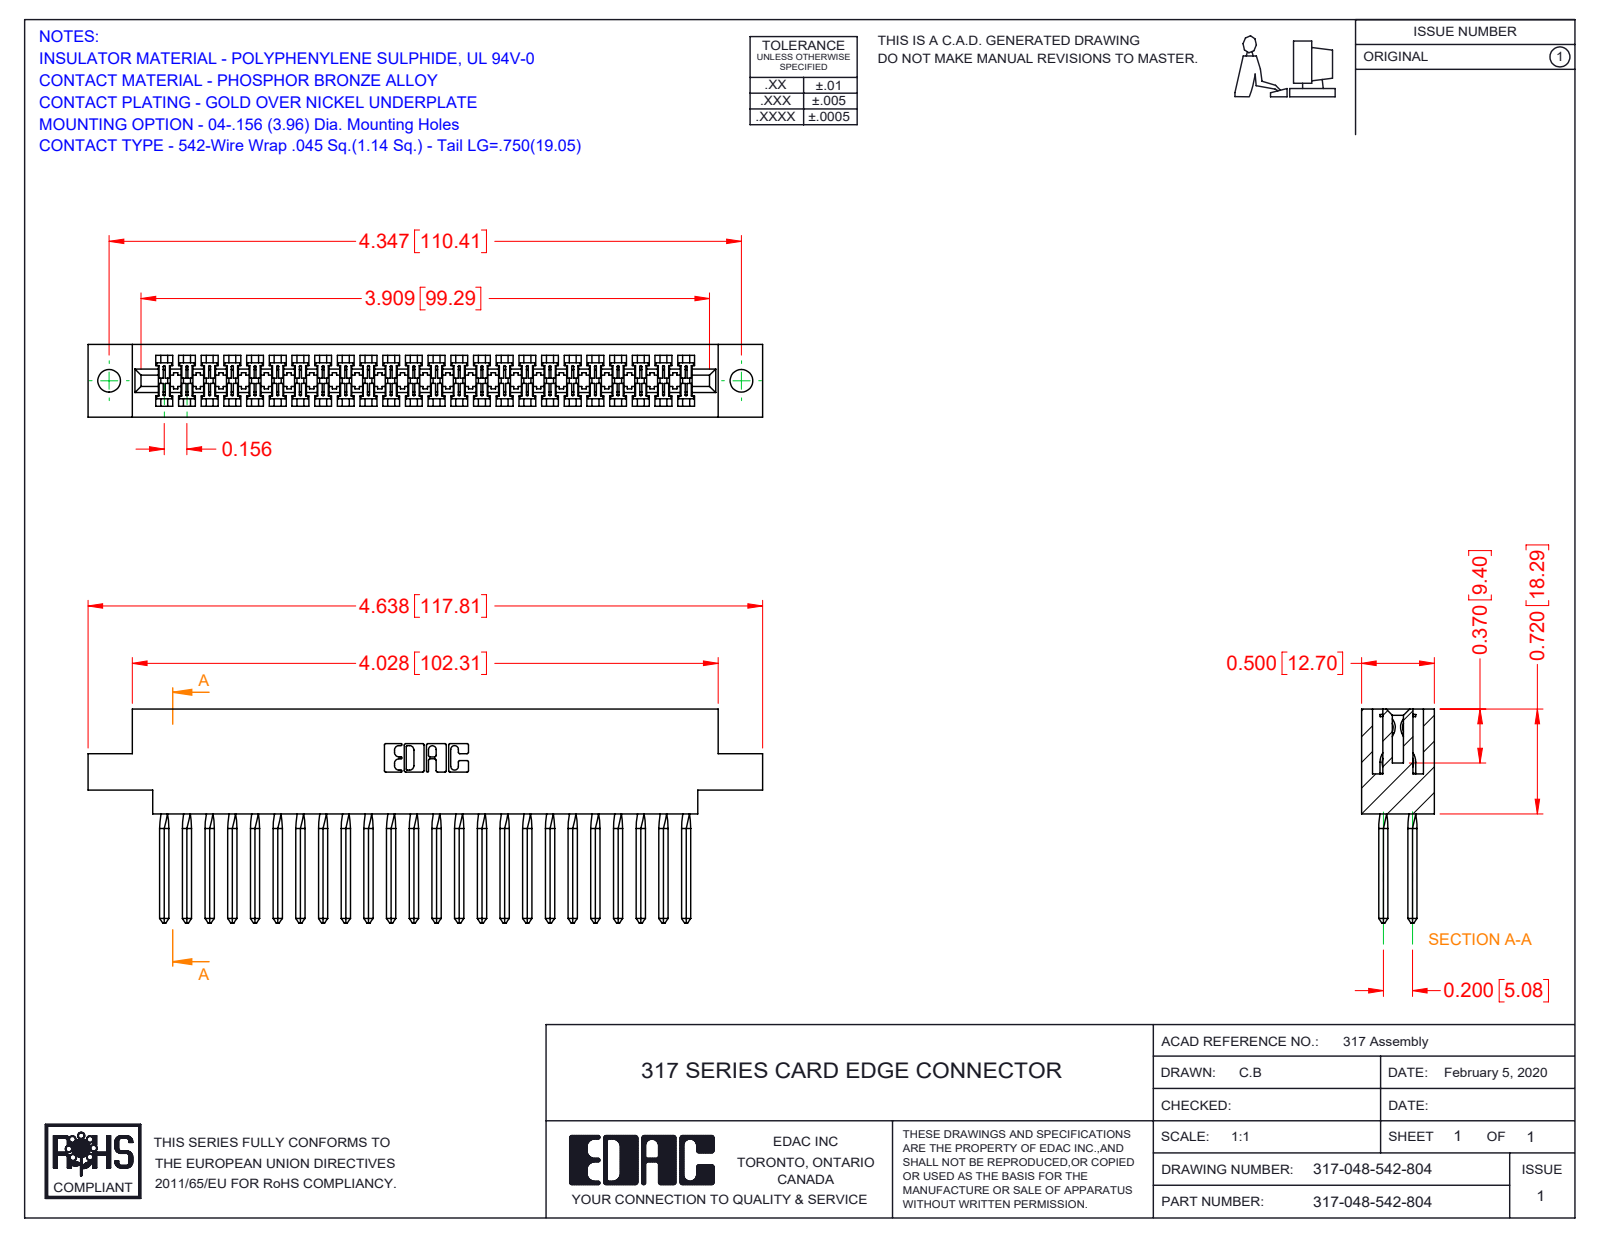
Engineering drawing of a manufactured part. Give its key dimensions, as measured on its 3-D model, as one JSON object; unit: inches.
{"part_name": "317-048-542-804; 317-290-003_542; 317 Part_.156 Dia - TH", "step_written_by": "SolidWorks 2016 (CONFIG_CONTROL_DESIGN)", "units": "inches", "bodies": {"solids": 49, "faces": 2838, "planar": 2266, "cylindrical": 380, "other": 192}, "overall_size": [4.638, 1.47, 0.5], "volume_in3": 1.137, "surface_area_in2": 38.98, "round_holes": [[0.156, 2]], "partial_cylinders_radius": [[0.006, 96], [0.01, 22], [0.007, 6], [0.031, 6], [0.026, 3], [0.074, 2], [0.089, 2], [0.1, 2]], "face_to_face_distances": [0.5, 0.075, 0.425, 0.35, 0.11, 0.2, 0.116, 0.046, 0.136, 0.72], "hole_center_spacings": [4.347]}
